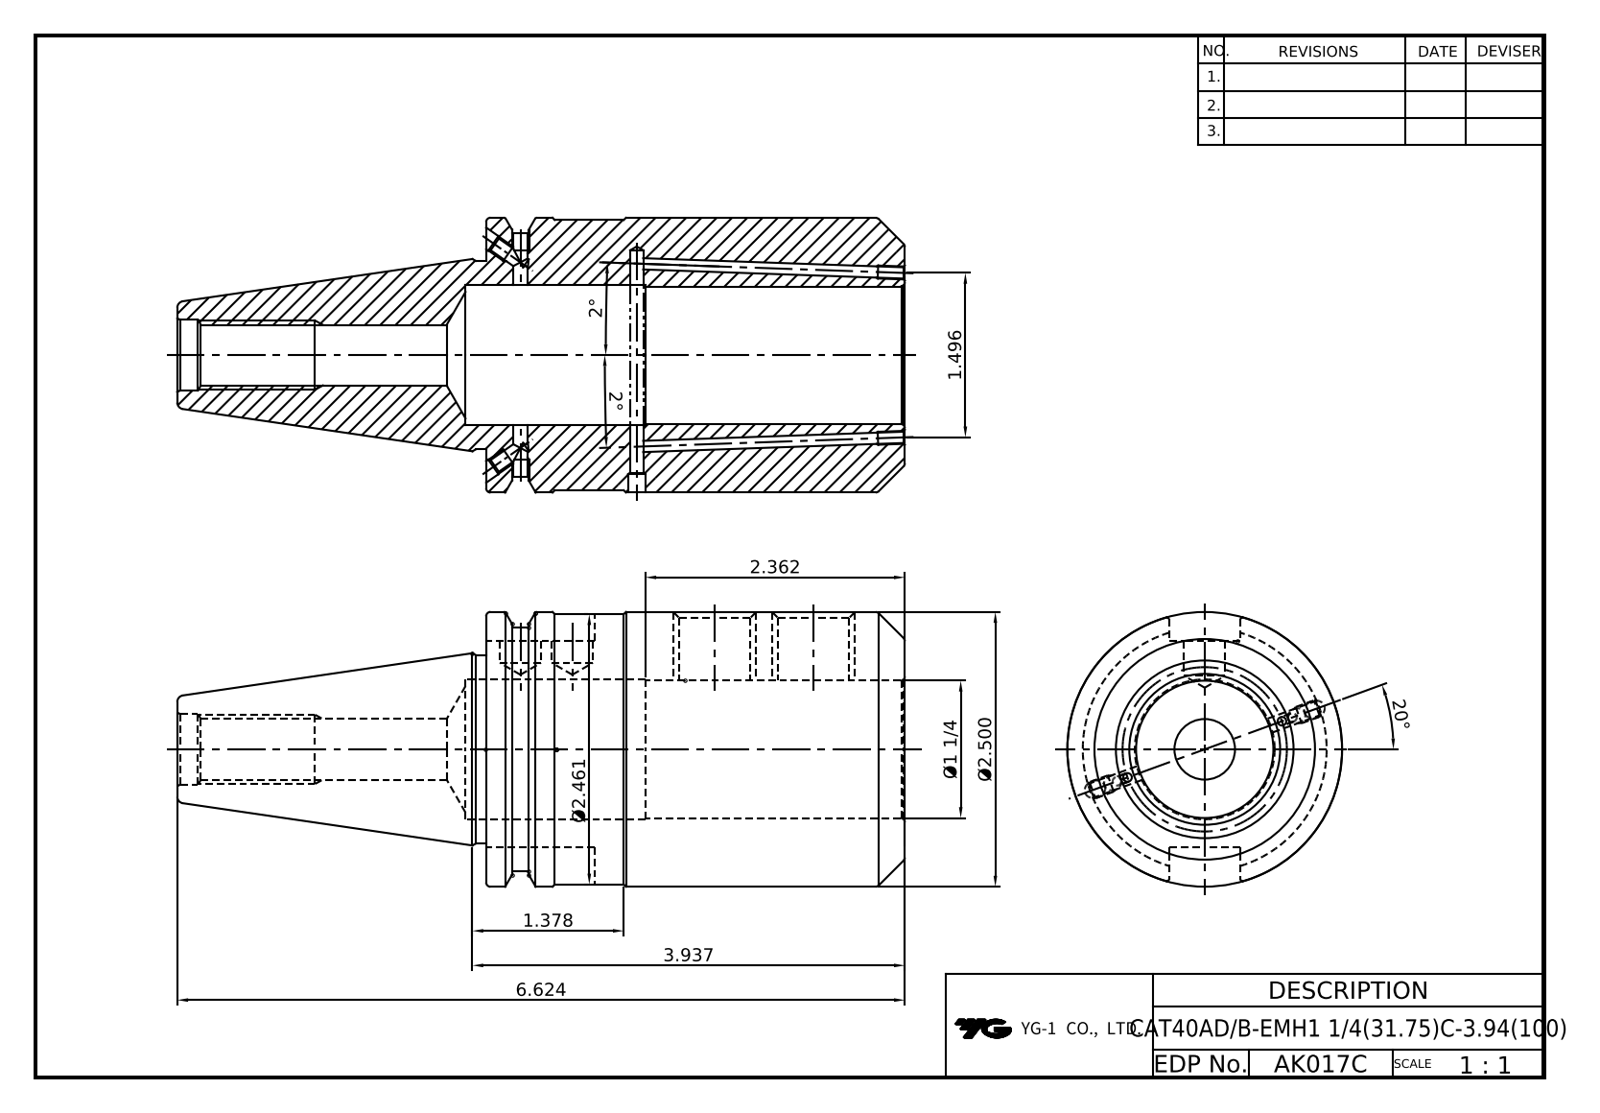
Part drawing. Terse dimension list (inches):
name: LO-CAT40ADB-EMH31.75C-100
written by: Autodesk Inventor 2022 (AUTOMOTIVE_DESIGN)
unit: in
bodies: 1 solid, 94 faces (34 planar, 34 cylindrical, 26 other)
size: 6.624 × 2.5 × 2.5
volume: 16.01 in³; area: 74.16 in²
holes: 4× ⌀0.128, 2× ⌀0.102, 2× ⌀0.157, 2× ⌀0.165, 2× ⌀0.682, 1× ⌀0.375, 1× ⌀0.527, 1× ⌀0.642, 1× ⌀1.25, 1× ⌀1.274
bosses: 1× ⌀2.5, 1× ⌀2.461, 1× ⌀1.717
rounds: 1× R0.322, 1× R1.108
face distances: 3.812, 0.188, 4, 1.874, 0.645, 2.624, 2.812, 6.624, 3.201, 0.577
hole spacings: 0.9, 1.768, 2.668
